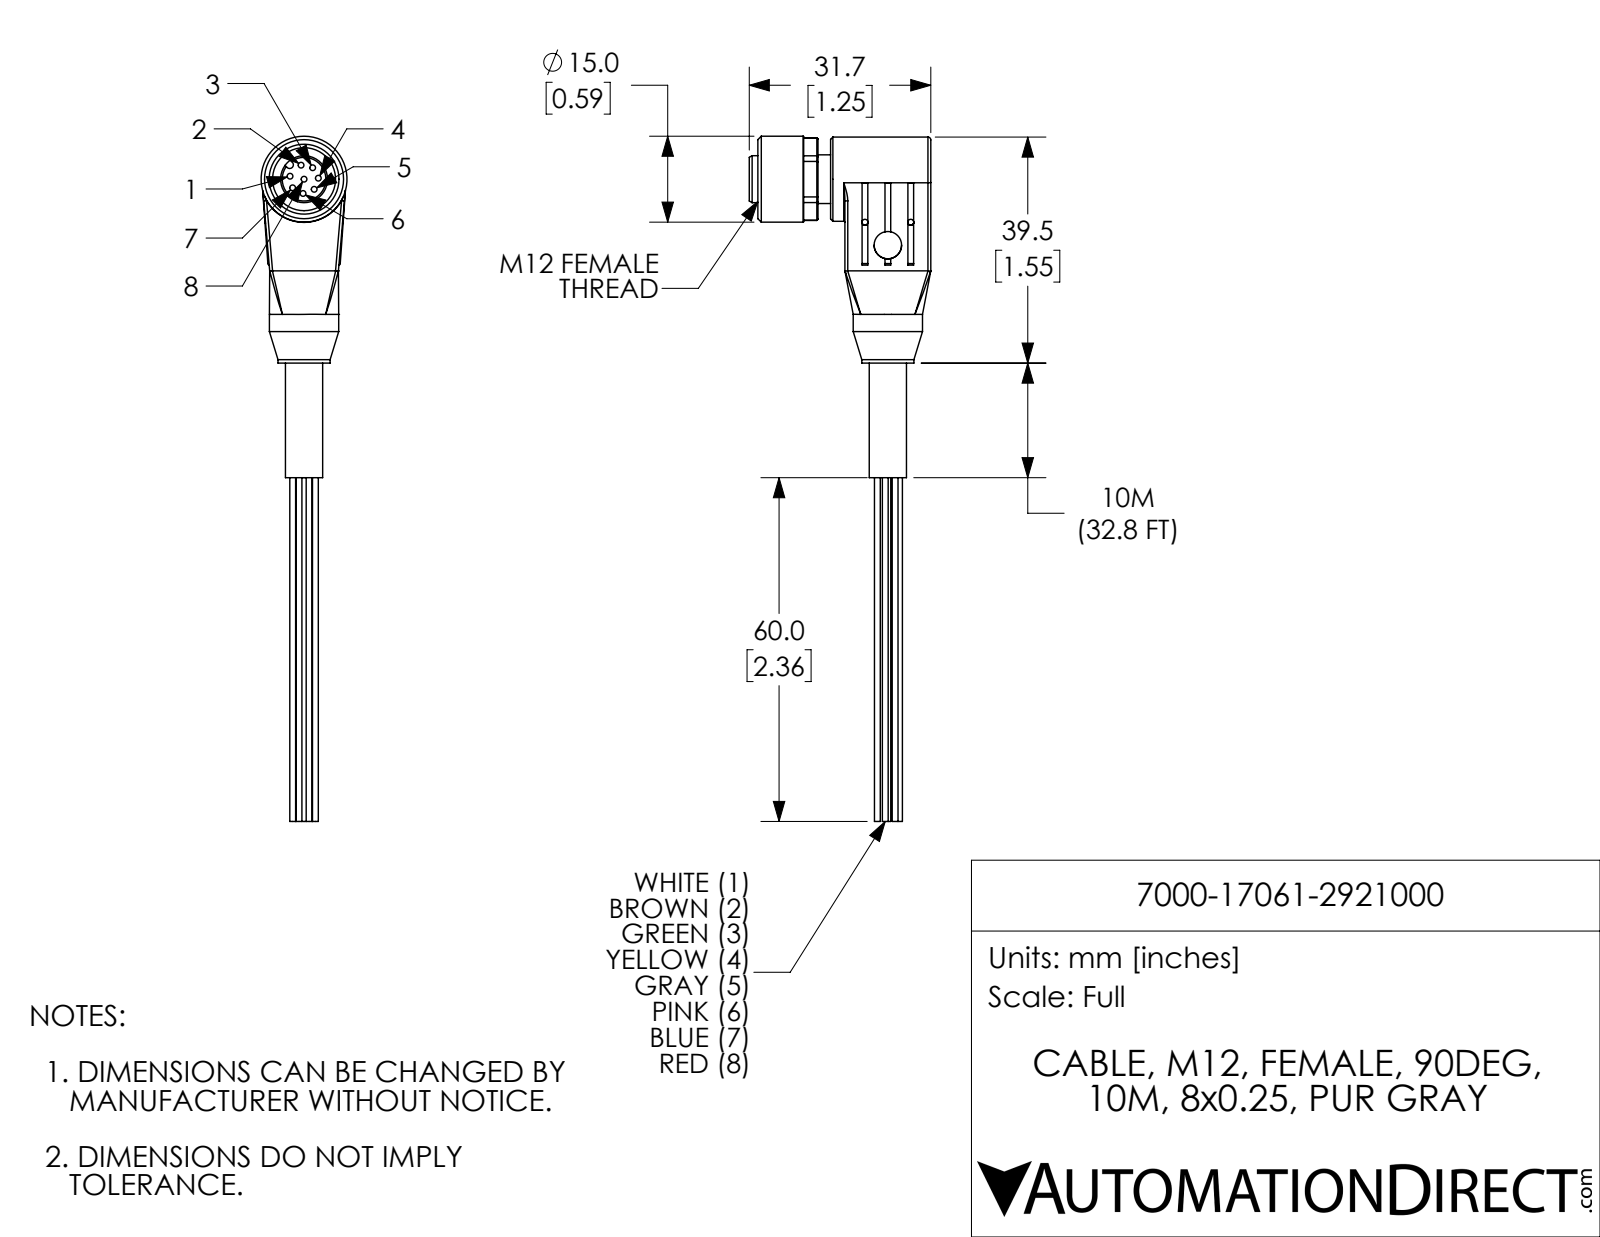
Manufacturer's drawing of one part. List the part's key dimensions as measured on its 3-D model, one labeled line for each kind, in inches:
Part name (STEP PRODUCT): 7000-17061-2921000
STEP written by: SolidWorks 2017 (AUTOMOTIVE_DESIGN)
Units: inches
Bodies: 1 solid, 189 faces (81 planar, 75 cylindrical, 33 other)
Overall size (bounding box): 4.709 × 1.248 × 0.591
Volume: 0.579 in³ · Surface area: 8.705 in²
Round holes (diameter × count): ⌀0.039 ×8, ⌀0.041 ×4, ⌀0.189 ×1, ⌀0.433 ×1
Round bosses / shafts (diameter × count): ⌀0.04 ×8, ⌀0.591 ×1, ⌀0.579 ×1, ⌀0.476 ×1, ⌀0.358 ×1, ⌀0.335 ×1, ⌀0.323 ×1, ⌀0.256 ×1
Partial cylindrical surfaces — rounded edges, fillets, slot ends (radius × count): R0.02 ×4, R0.012 ×2, R0.026 ×1, R0.283 ×1
Main face-to-face distances: 0.098, 0.591, 0.185, 0.689, 0.776, 0.087, 0.118, 0.303, 0.472, 0.657
Hole centre spacings: 0.098, 0.081, 0.149, 0.195, 0.082, 0.166, 0.189, 0.189
